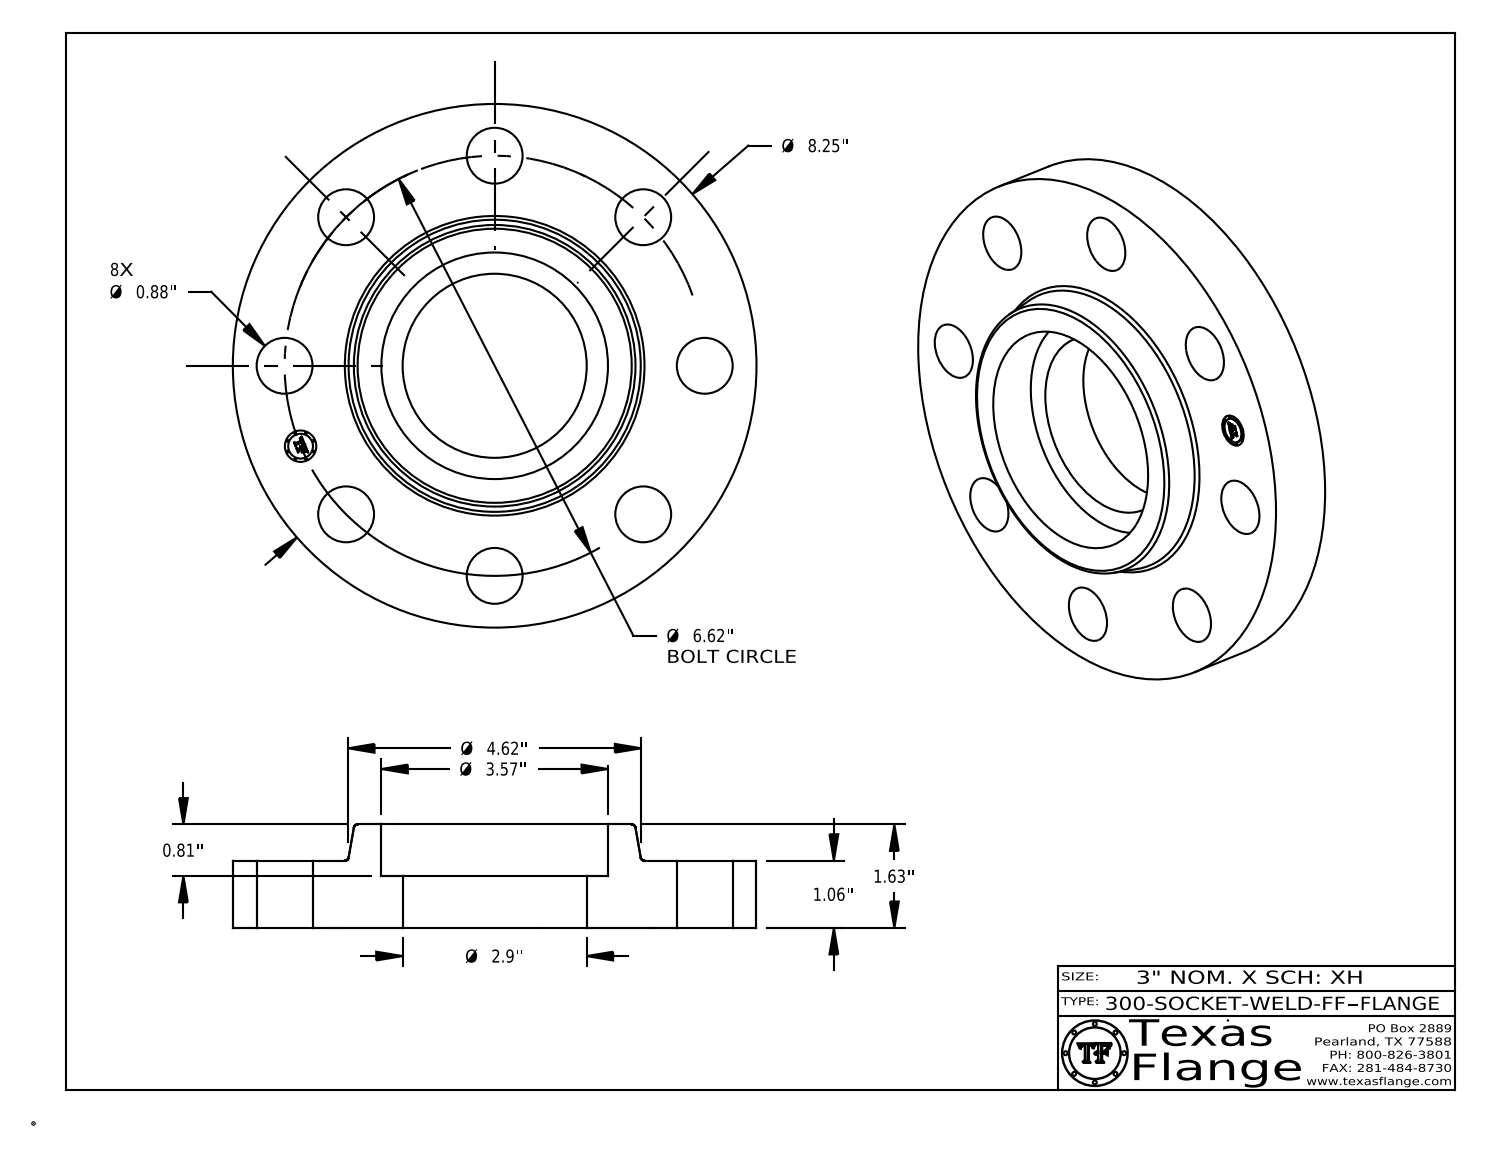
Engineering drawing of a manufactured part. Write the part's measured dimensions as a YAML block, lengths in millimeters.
part_name: "300-SOCKET-WELD-FF"
step_written_by: "CATIA V5 STEP AP214 (AUTOMOTIVE_DESIGN)"
units: millimeters
bodies: {solids: 1, faces: 418, planar: 370, cylindrical: 42, other: 6}
overall_size: [209.6, 209.6, 41.4]
volume: 772300
surface_area: 101800
round_holes:
  - {diameter: 22.4, count: 8}
  - {diameter: 12.6, count: 1}
  - {diameter: 73.7, count: 1}
  - {diameter: 90.7, count: 1}
round_bosses_or_shafts:
  - {diameter: 0.8, count: 8}
  - {diameter: 209.6, count: 1}
  - {diameter: 9.9, count: 1}
face_to_face_distances: [26.9, 41.4, 14.5, 20.8, 6.1, 20.6, 0.4, 26.5, 5.7, 14.9]
hole_center_spacings: [84.1, 64.3, 155.3, 118.9, 118.9, 32.8, 93.4, 164.9]
